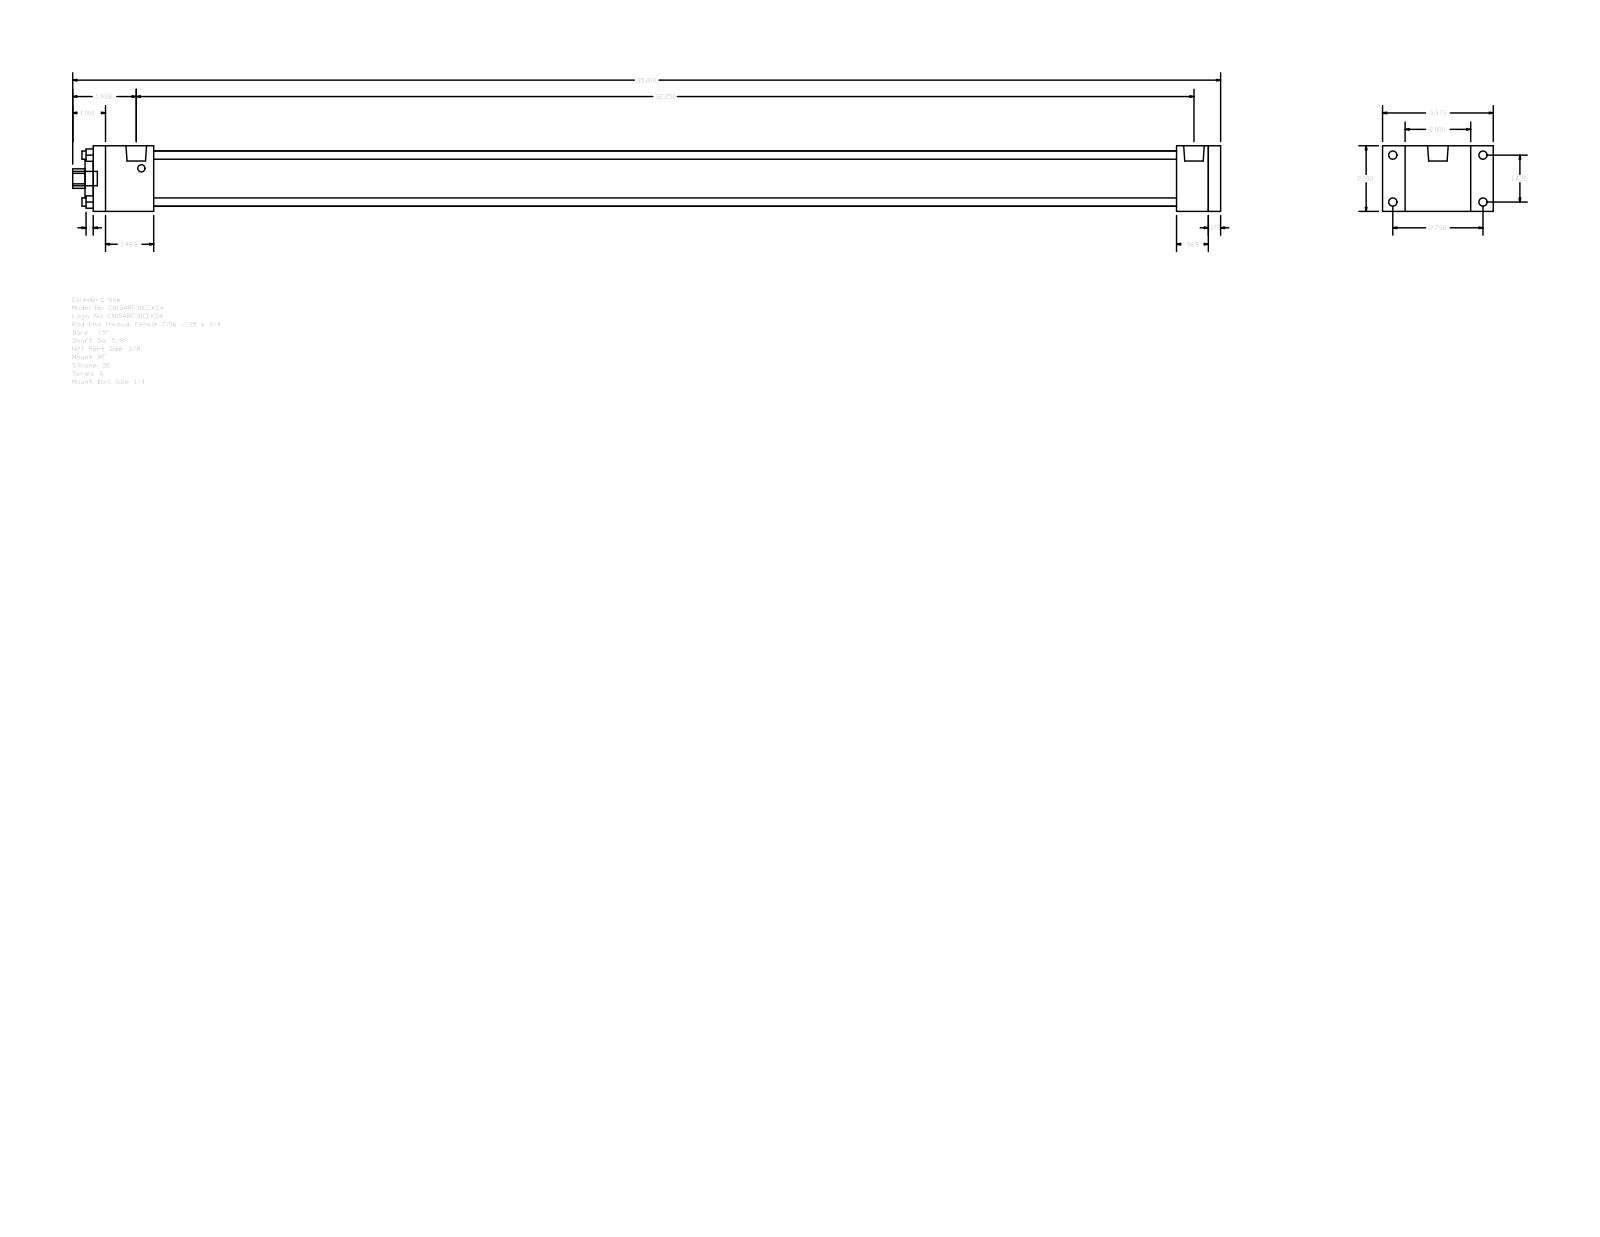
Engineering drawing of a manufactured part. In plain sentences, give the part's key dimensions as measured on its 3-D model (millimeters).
The part is named "A_RF__0150_0.625". Its 3-D file was written by "GSSL Pune (CONFIG_CONTROL_DESIGN)". It is 0 solids with 92 faces: 64 planar, 28 cylindrical and 0 other. Overall it measures 889 by 85.72 by 50.8 millimeters. Round holes: 4 of diameter 6.35, 1 of diameter 15.88, 1 of diameter 28.57, 1 of diameter 42.93. Round bosses or shafts: 4 of diameter 6.35, 4 of diameter 5.56, 2 of diameter 15.93, 1 of diameter 11.11. Partial cylindrical surfaces (rounded edges, fillets, slot ends): 1 of radius 7.54. The main face-to-face distances are 50.8, 9.52, 863.6, 873.12, 838.99, 24.61, 34.13, 46.83, 792.16, 816.77. The hole center spacings are 25.68, 36.32, 51.36.
